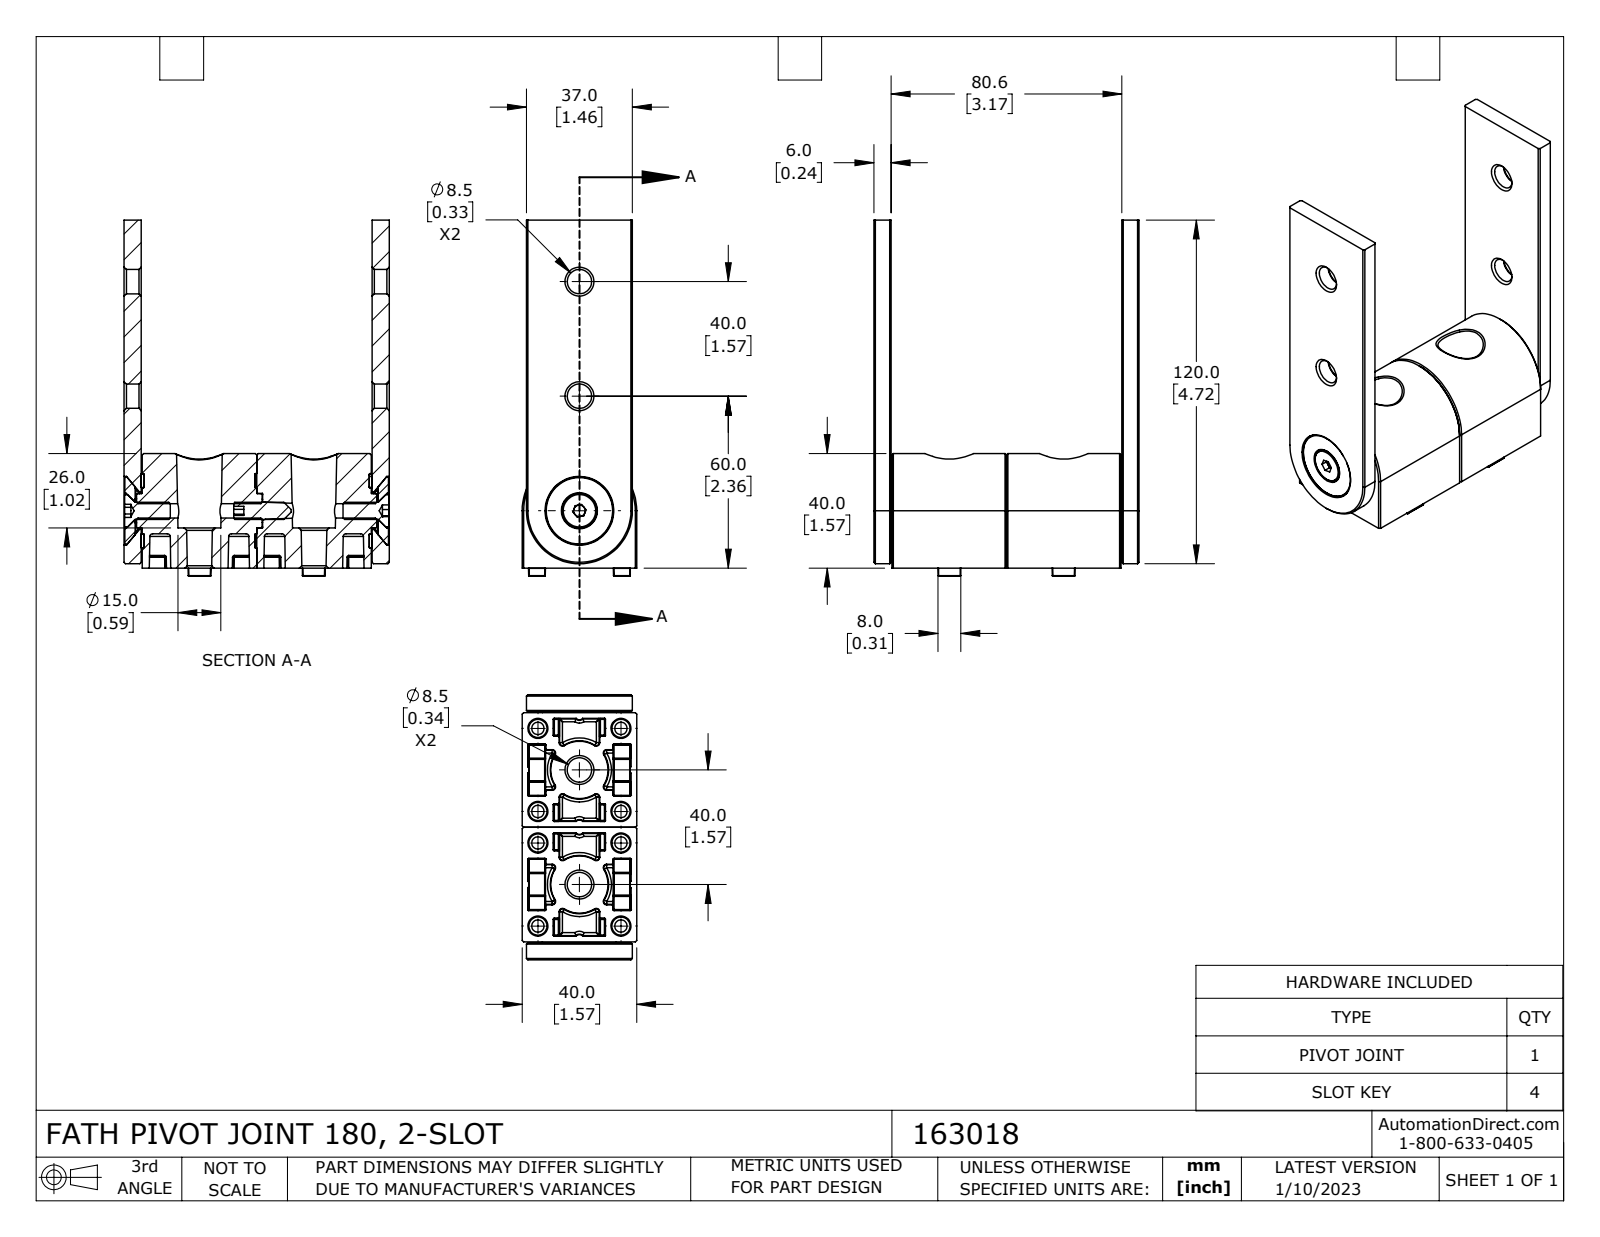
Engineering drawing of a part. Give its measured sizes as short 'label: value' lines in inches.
name: 163018
written by: SolidWorks 2021 (CONFIG_CONTROL_DESIGN)
unit: in
bodies: 15 solids, 1539 faces (359 planar, 512 cylindrical, 668 other)
size: 4.894 × 3.646 × 1.575
volume: 8.398 in³; area: 87.57 in²
holes: 2× ⌀0.079, 2× ⌀0.335, 1× ⌀0.197, 1× ⌀0.252, 1× ⌀0.48, 1× ⌀0.512, 1× ⌀0.638, 1× ⌀0.945, 1× ⌀1.024
bosses: 1× ⌀1.016, 1× ⌀0.929, 1× ⌀0.63, 1× ⌀0.446, 1× ⌀0.236
rounds: 148× R0.008, 92× R0.012, 12× R0.039, 2× R0.038, 1× R0.181, 1× R0.728, 1× R0.787
face distances: 0.236, 3.409, 1.823, 1.587, 1.575, 3.173, 3.646, 0.059, 1.516, 0.248
hole spacings: 0.413, 1.575, 1.628, 3.177, 0.827, 3.15
